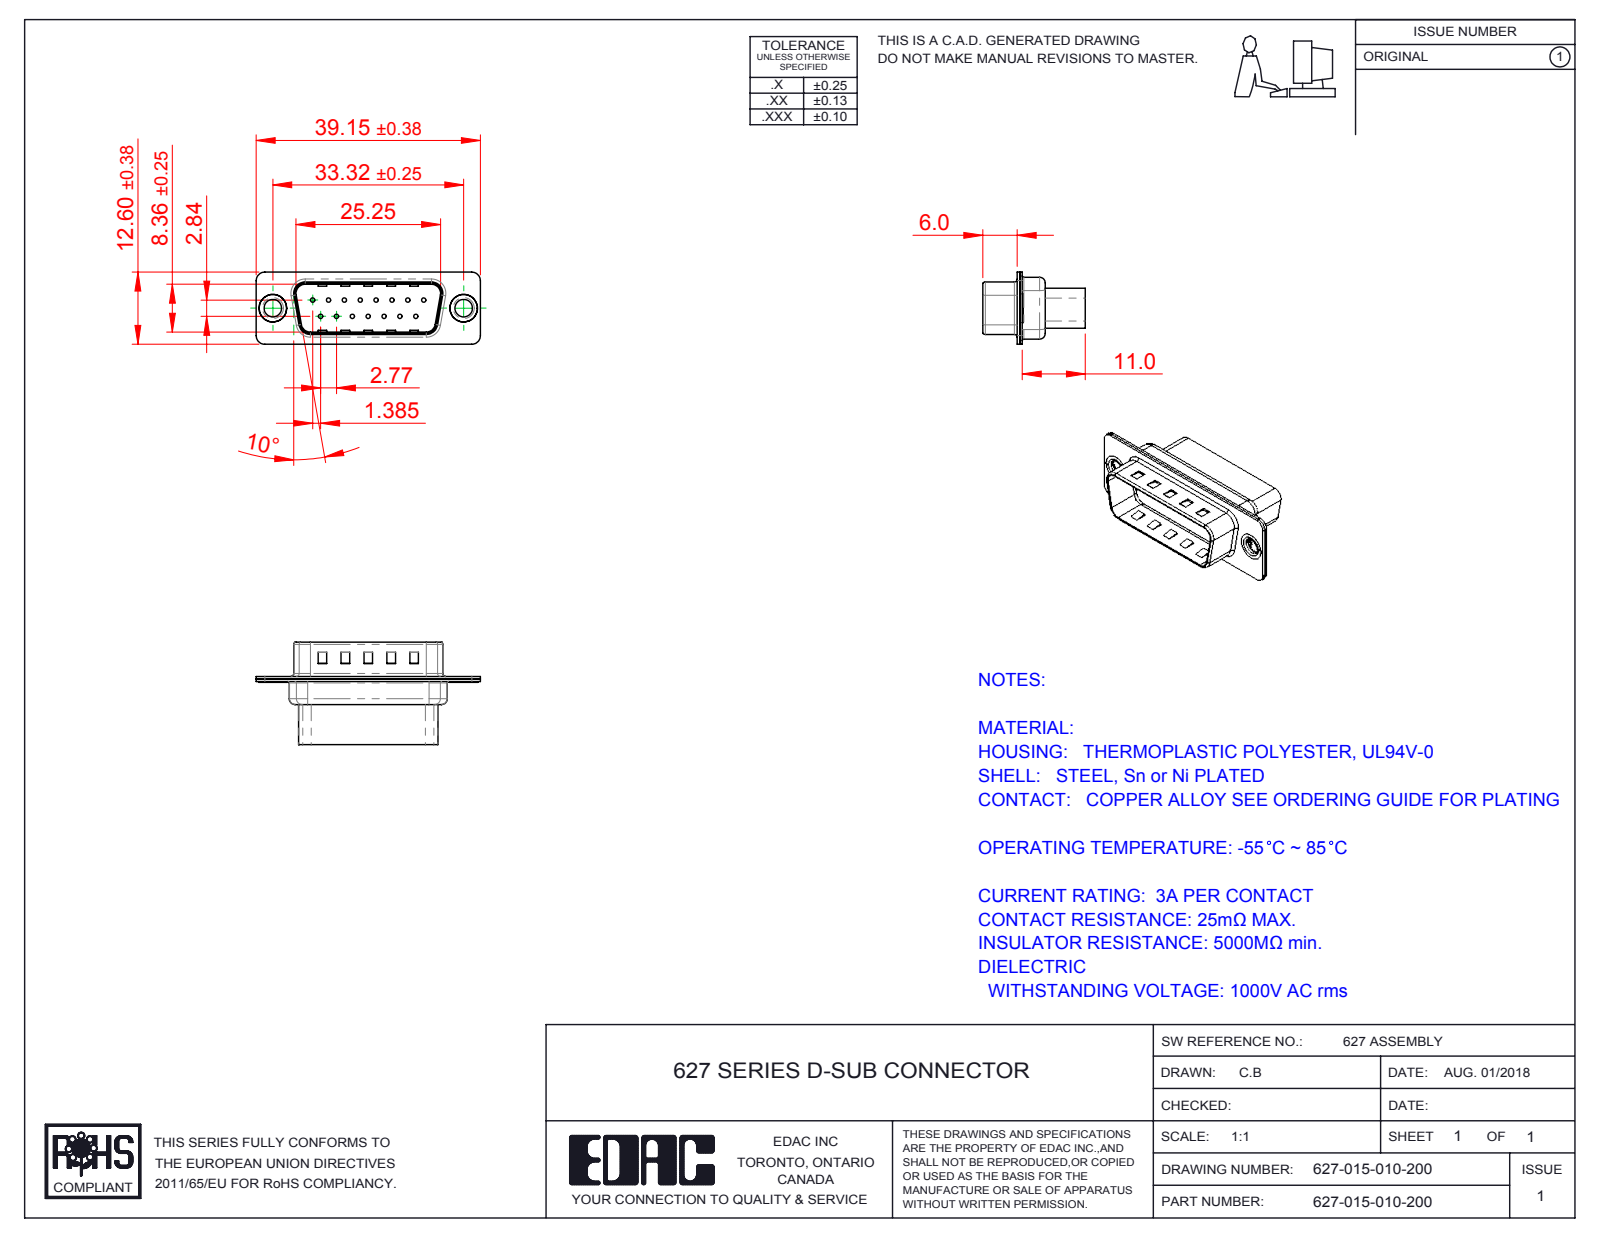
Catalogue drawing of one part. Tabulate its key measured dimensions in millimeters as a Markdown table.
| quantity | value |
| --- | --- |
| part name | 627 Housing_15 HP; 627-015-010-200; 627 Thru Hole Rivet; 627 Shell Rear_15 Contacts (+1 more) |
| STEP written by | SolidWorks 2016 (CONFIG_CONTROL_DESIGN) |
| units | millimeters |
| bodies | 5 solids, 434 faces (169 planar, 207 cylindrical, 58 other) |
| overall size | 39.15 × 17.9 × 12.6 |
| volume | 2 353 mm³ |
| surface area | 4 638 mm² |
| round holes (diameter × count) | 0.75 × 15, 1.6 × 15, 2 × 15, 3.05 × 2, 4 × 2, 4.8 × 2 |
| round bosses / shafts (diameter × count) | 5 × 2, 4.9 × 2, 3.55 × 2 |
| partial cylindrical surfaces (radius × count) | 1.5 × 16, 2 × 12, 0.5 × 8, 1.6 × 8, 0.25 × 4, 0.6 × 4, 0.65 × 4, 0.9 × 4 |
| main face-to-face distances | 0.4, 0.45, 0.9, 0.82, 9.58, 0.68, 7.68, 1.08, 8.08, 8.76 |
| hole center spacings | 3.16, 2.77, 5.54, 8.31, 11.08, 5.03, 5.04, 7.48 |
